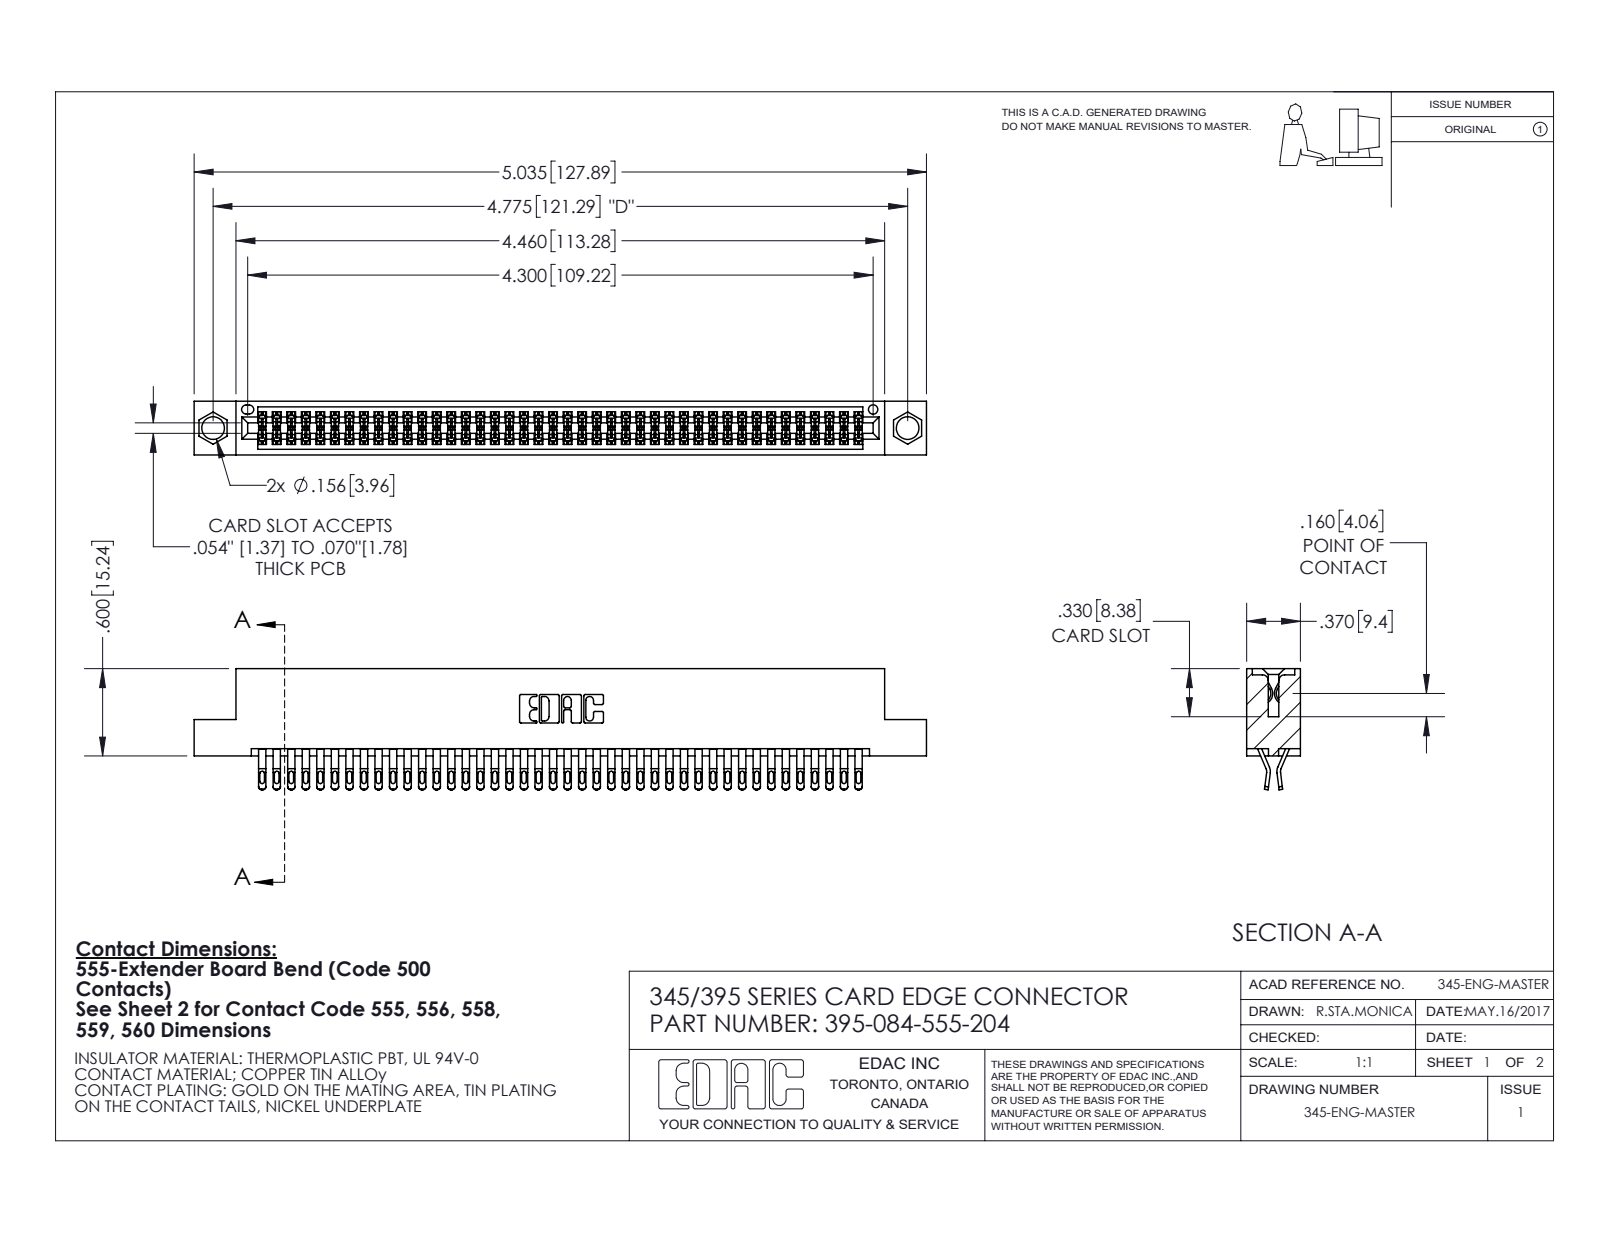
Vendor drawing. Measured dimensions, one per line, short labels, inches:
name: 345-292-001_555 Tail; 395-084-555-204; 345 Part_Flush Mounting Lugs - 0.156 Dia-TI
written by: SolidWorks 2020 (CONFIG_CONTROL_DESIGN)
unit: in
bodies: 85 solids, 4844 faces (2698 planar, 2146 cylindrical, 0 other)
size: 5.035 × 0.832 × 0.37
volume: 0.767 in³; area: 29.86 in²
holes: 2× ⌀0.156, 1× ⌀0.064
rounds: 210× R0.016, 168× R0.006, 168× R0.02, 22× R0.01, 6× R0.007, 6× R0.031, 3× R0.026, 2× R0.01
face distances: 0.298, 0.072, 0.2, 0.025, 0.37, 0.098, 0.272, 0.225, 0.175, 0.149
hole spacings: 0.27, 4.539, 4.775
